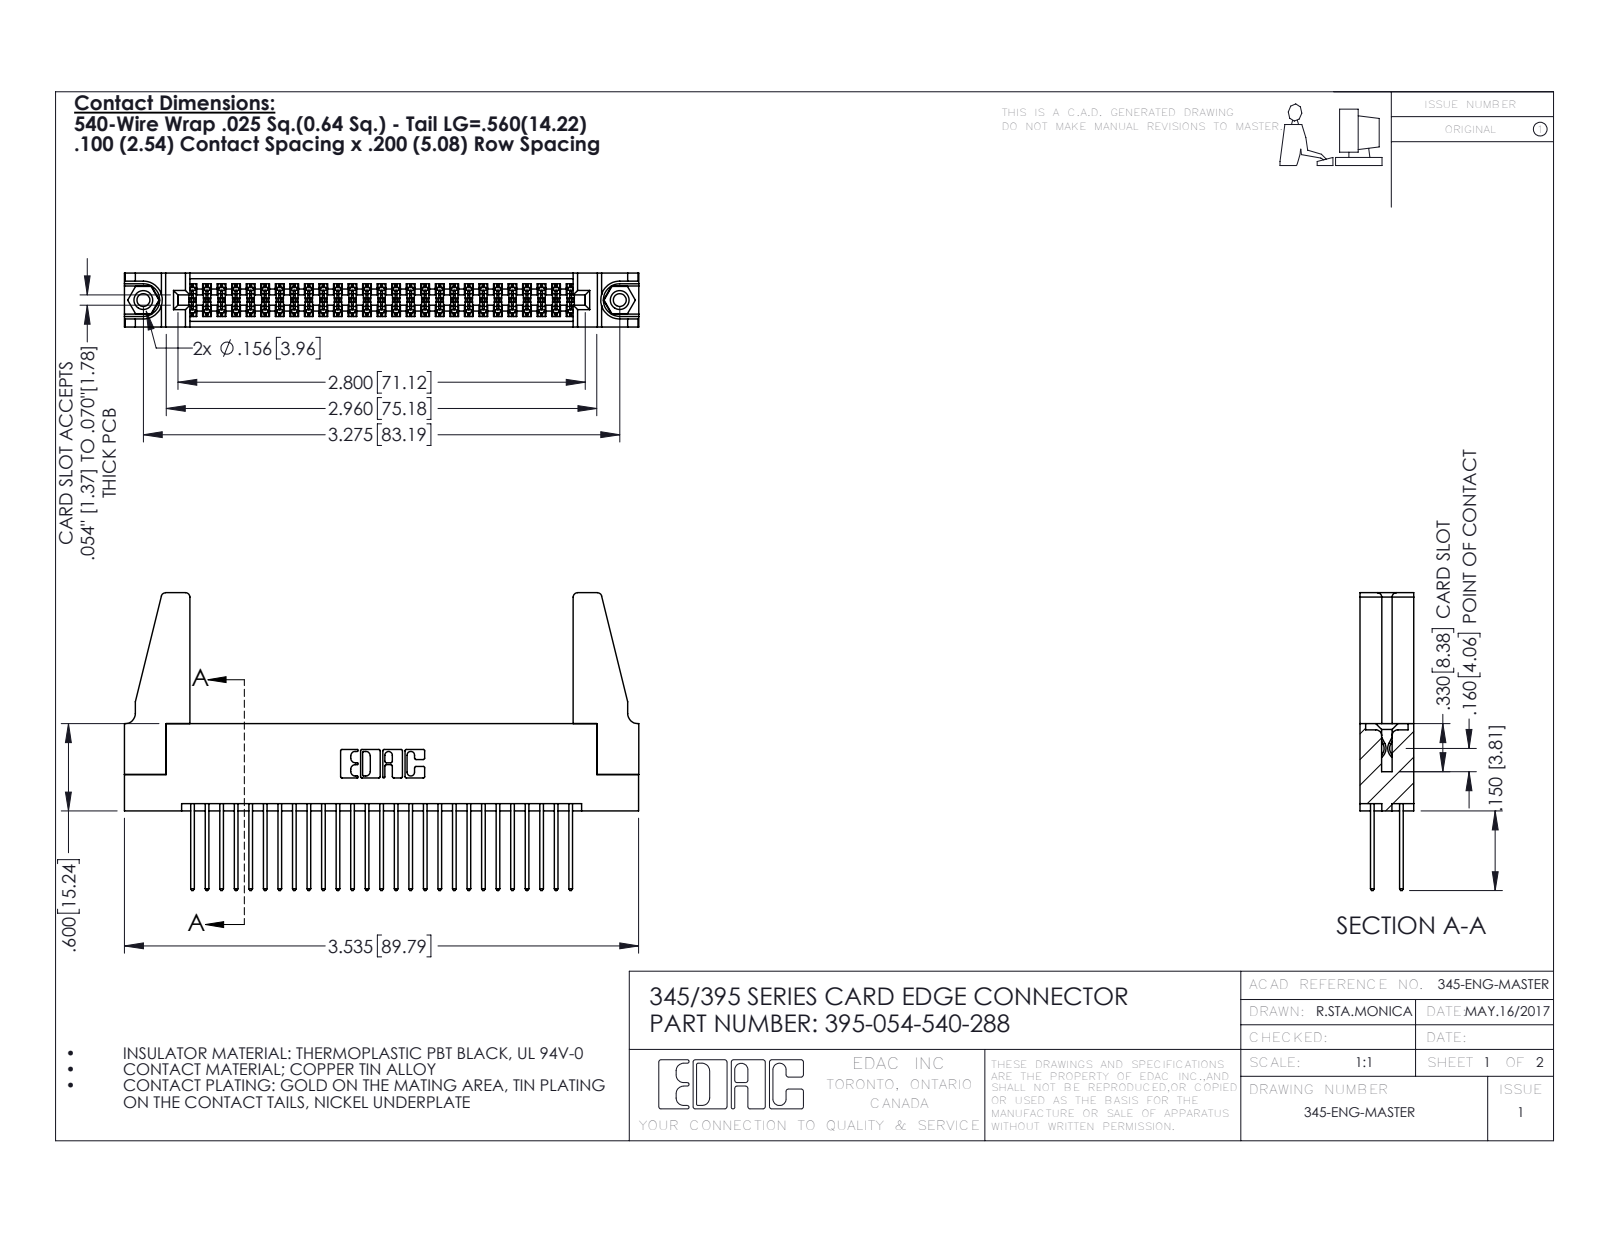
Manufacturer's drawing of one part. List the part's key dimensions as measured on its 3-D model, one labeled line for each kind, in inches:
Part name (STEP PRODUCT): 345-292-001_345-293-140; 345-220-078_345-220-088; 395-054-540-288; 345-250-001_345-250-001-102 (+1 more)
STEP written by: SolidWorks 2016 (CONFIG_CONTROL_DESIGN)
Units: inches
Bodies: 59 solids, 2950 faces (1934 planar, 1000 cylindrical, 16 other)
Overall size (bounding box): 3.536 × 2.047 × 0.37
Volume: 0.735 in³ · Surface area: 26 in²
Round holes (diameter × count): ⌀0.089 ×2, ⌀0.125 ×2, ⌀0.156 ×2, ⌀0.064 ×1
Round bosses / shafts (diameter × count): ⌀0.155 ×2
Partial cylindrical surfaces — rounded edges, fillets, slot ends (radius × count): R0.006 ×81, R0.01 ×54, R0.01 ×22, R0.03 ×8, R0.007 ×6, R0.031 ×6, R0.026 ×3, R0.014 ×2
Main face-to-face distances: 0.072, 0.298, 0.2, 0.37, 0.098, 0.272, 0.025, 0.225, 0.175, 0.149
Hole centre spacings: 0.27, 3.04, 3.275
